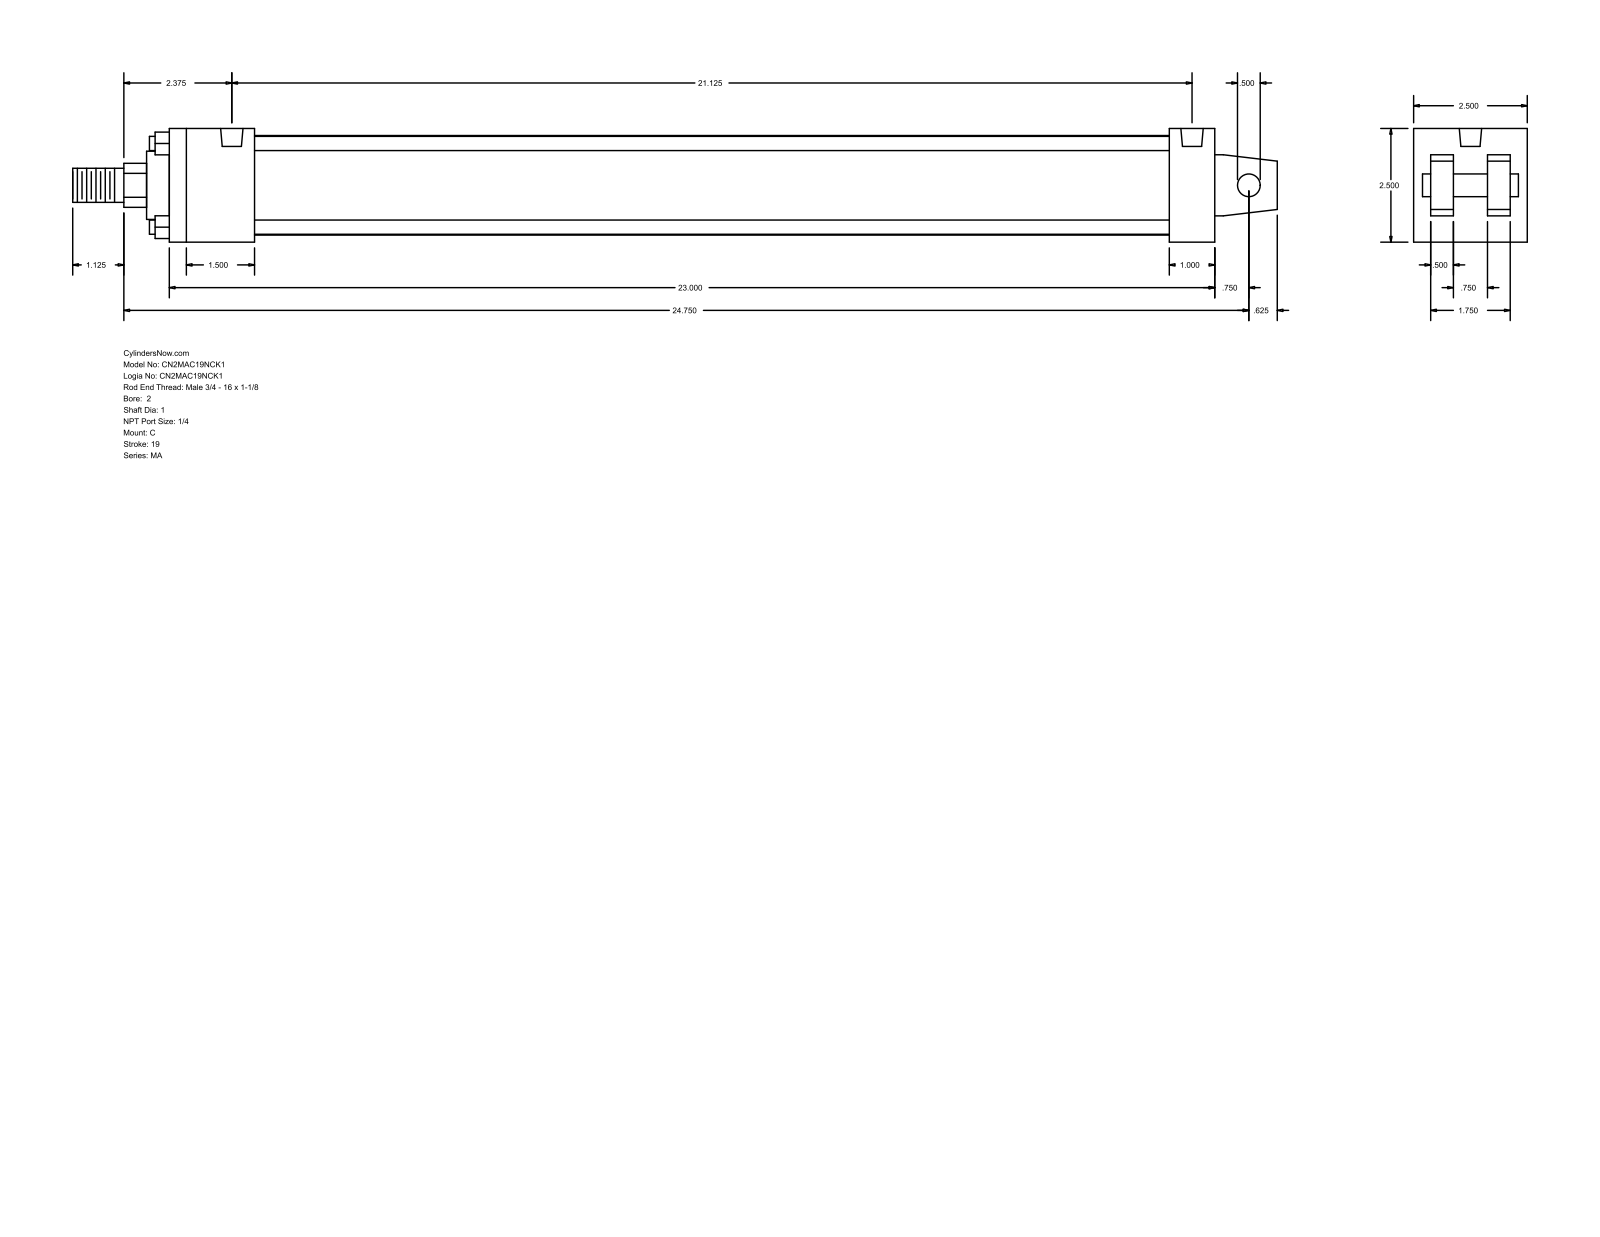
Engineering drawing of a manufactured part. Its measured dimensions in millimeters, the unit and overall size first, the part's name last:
Units: millimetres
Overall size (bounding box): 673.1 × 63.5 × 63.5
Round holes (diameter × count): ⌀7.94 ×4, ⌀12.49 ×2
Round bosses / shafts (diameter × count): ⌀7.94 ×4, ⌀55.63 ×1, ⌀38.1 ×1, ⌀25.4 ×1, ⌀19.05 ×1, ⌀12.7 ×1
Partial cylindrical surfaces — rounded edges, fillets, slot ends (radius × count): R12.29 ×1
Main face-to-face distances: 63.5, 12.7, 584.2, 22.22, 41.28, 9.52, 53.98, 31.76, 47.63, 25.4
Hole centre spacings: 536.57
Bodies: 0 solids, 103 faces (76 planar, 27 cylindrical, 0 other)
Part name (STEP PRODUCT): MA_C__0200_1
STEP written by: GSSL Pune (CONFIG_CONTROL_DESIGN)
